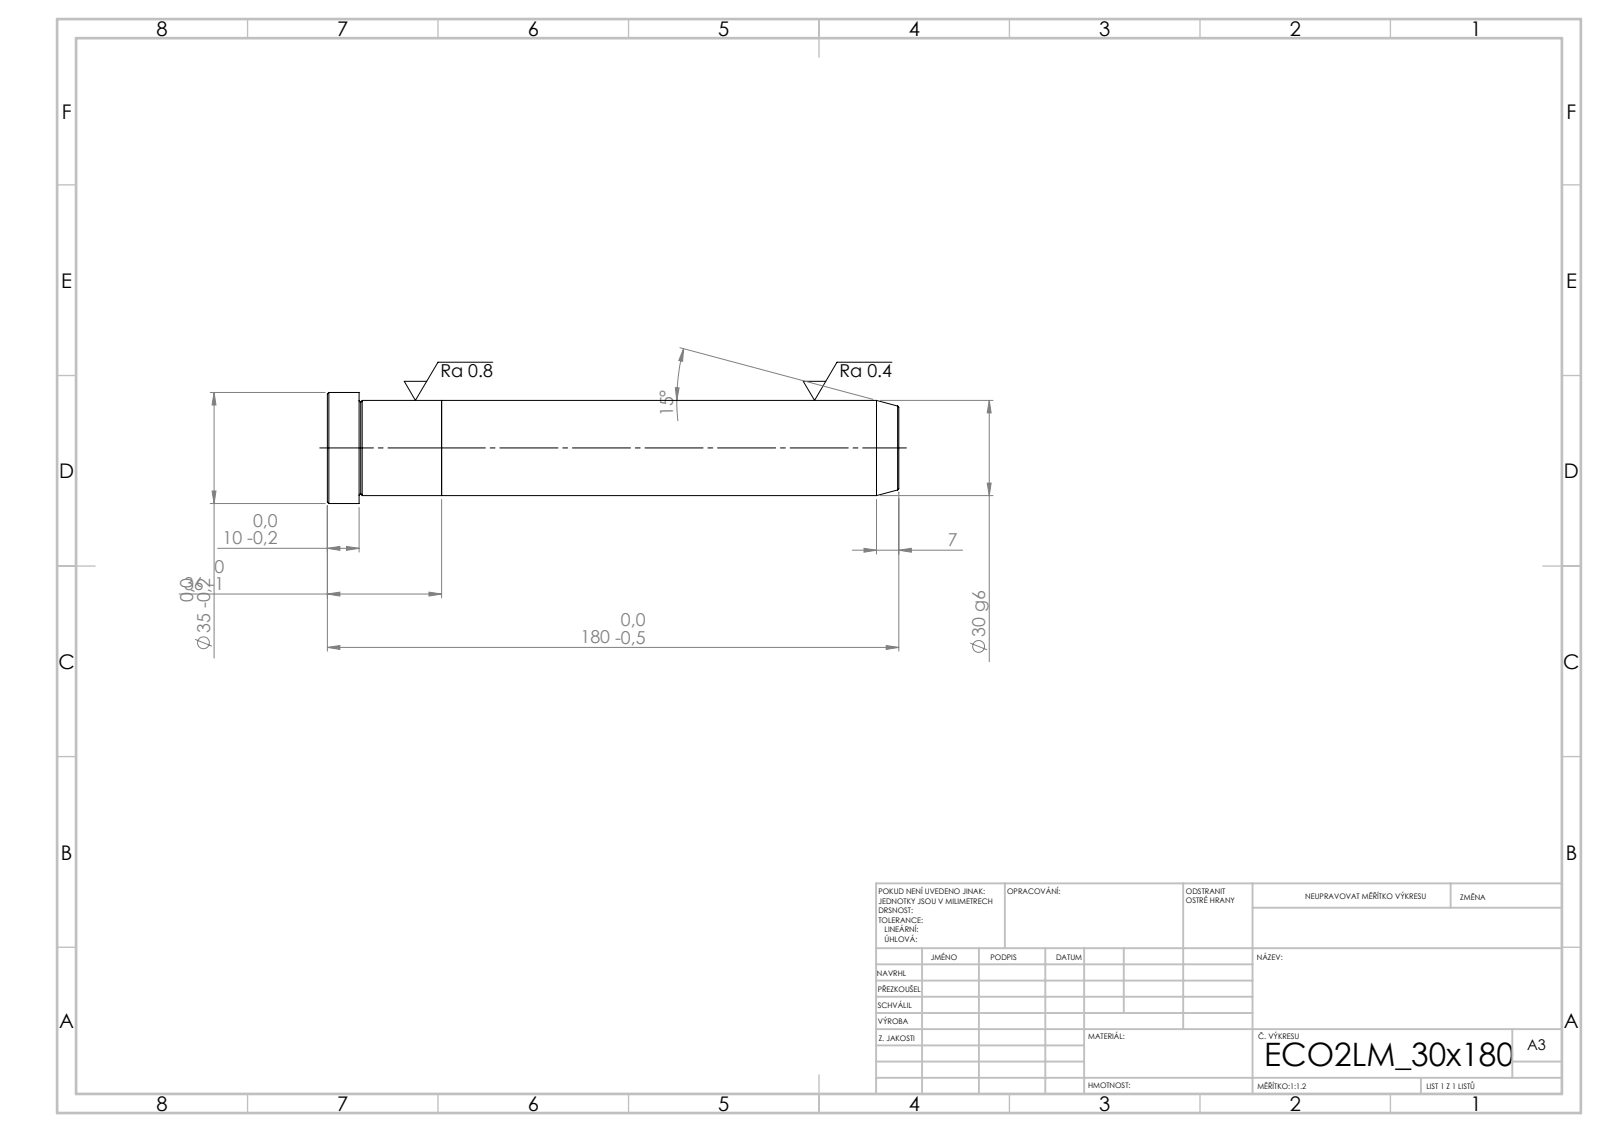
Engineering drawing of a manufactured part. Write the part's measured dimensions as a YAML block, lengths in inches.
step_written_by: "SolidWorks 2019 (CONFIG_CONTROL_DESIGN)"
units: inches
bodies: {solids: 2, faces: 21, planar: 5, cylindrical: 6, other: 10}
overall_size: [7.087, 1.378, 1.378]
volume: 7.881
surface_area: 31.44
round_bosses_or_shafts:
  - {diameter: 1.378, count: 1}
  - {diameter: 1.181, count: 1}
face_to_face_distances: [1.417, 5.669, 7.087, 6.693, 1.024, 0.394]
